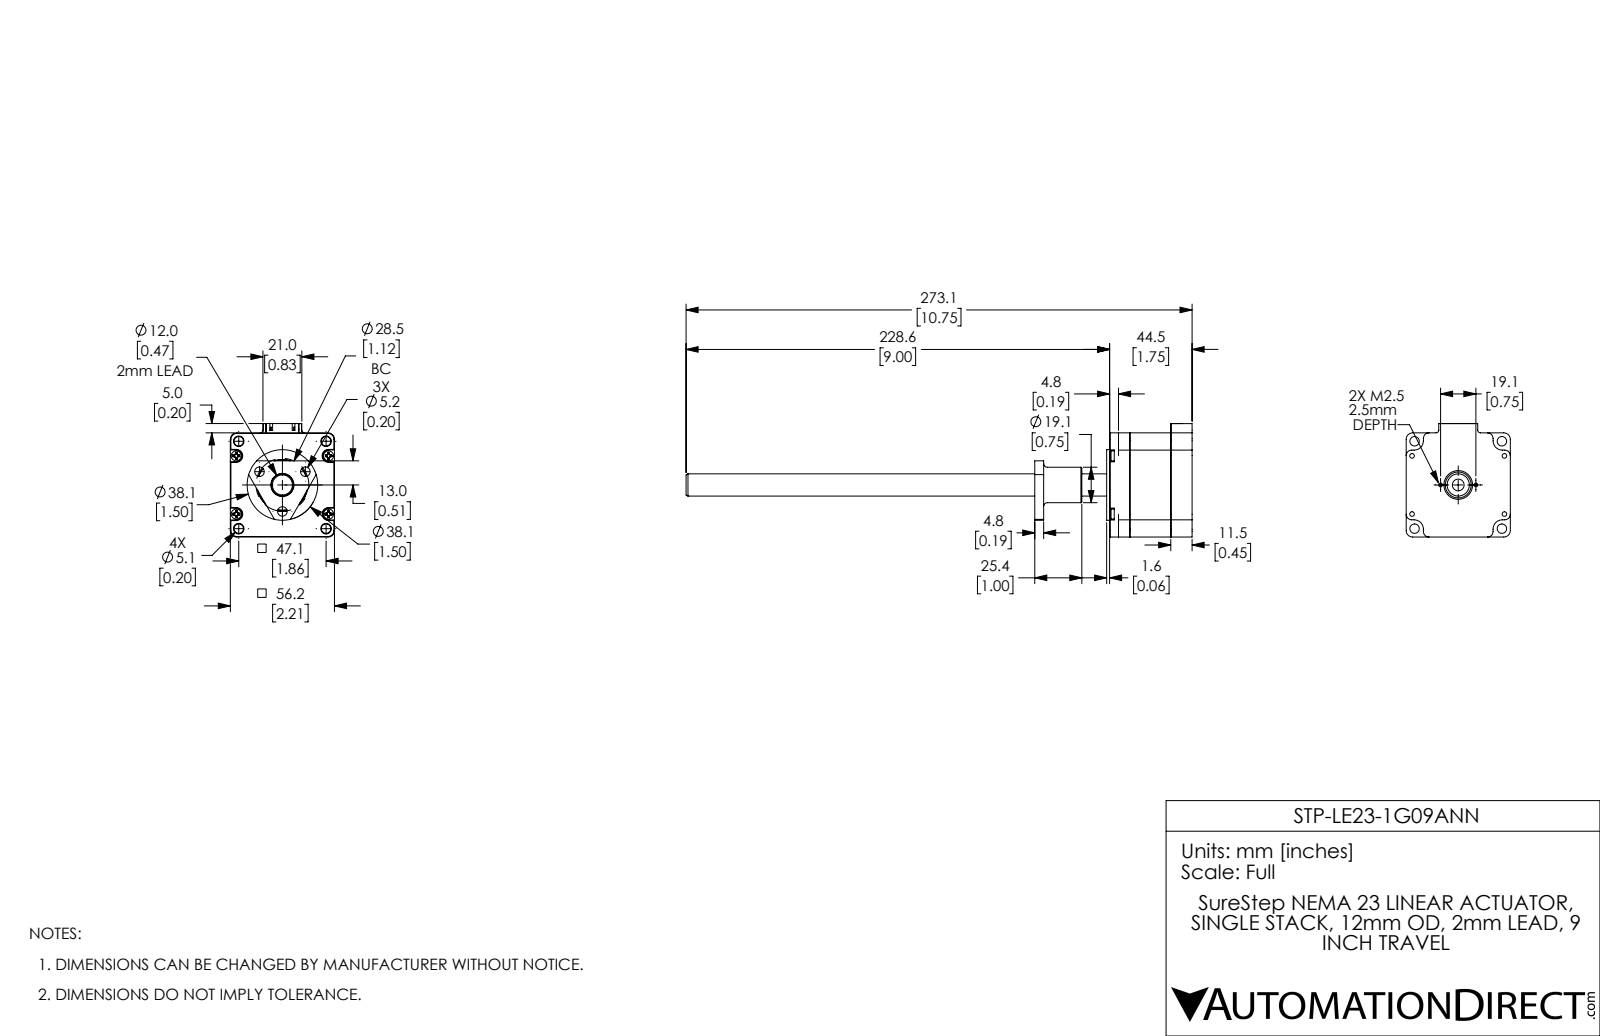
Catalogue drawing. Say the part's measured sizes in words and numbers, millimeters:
The part is named "STP-LE23-1G09ANN_1; STP-LE23-1G09ANN; STP-LE23-1G09ANN_2". Its 3-D file was written by "SolidWorks 2017 (AUTOMOTIVE_DESIGN)". It is 8 solids with 712 faces: 282 planar, 199 cylindrical and 231 other. Overall it measures 273.1 by 61.22 by 56.2 millimeters. Its volume is 132 789 cubic millimeters and its surface area 53 025 square millimeters. Round holes: 8 of diameter 4.5, 4 of diameter 2.5, 4 of diameter 3.3, 4 of diameter 5.1, 3 of diameter 5.16, 2 of diameter 2, 2 of diameter 2.05, 1 of diameter 6.35, 1 of diameter 6.8, 1 of diameter 10.5, 1 of diameter 15.5, 1 of diameter 20. Round bosses or shafts: 4 of diameter 5.4, 1 of diameter 38.1, 1 of diameter 36, 1 of diameter 35.6, 1 of diameter 34.85, 1 of diameter 19.1, 1 of diameter 16, 1 of diameter 12. Partial cylindrical surfaces (rounded edges, fillets, slot ends): 10 of radius 1.5, 8 of radius 3, 4 of radius 1.8, 4 of radius 3.2, 4 of radius 3.5, 4 of radius 5, 1 of radius 19.3. The main face-to-face distances are 22, 44.5, 56.2, 11.5, 33.5, 1.6, 51.4, 11, 33, 38.8. The hole center spacings are 14.12, 24.75, 33.05, 35.01, 45.74, 48.53, 56.99, 6.55.
